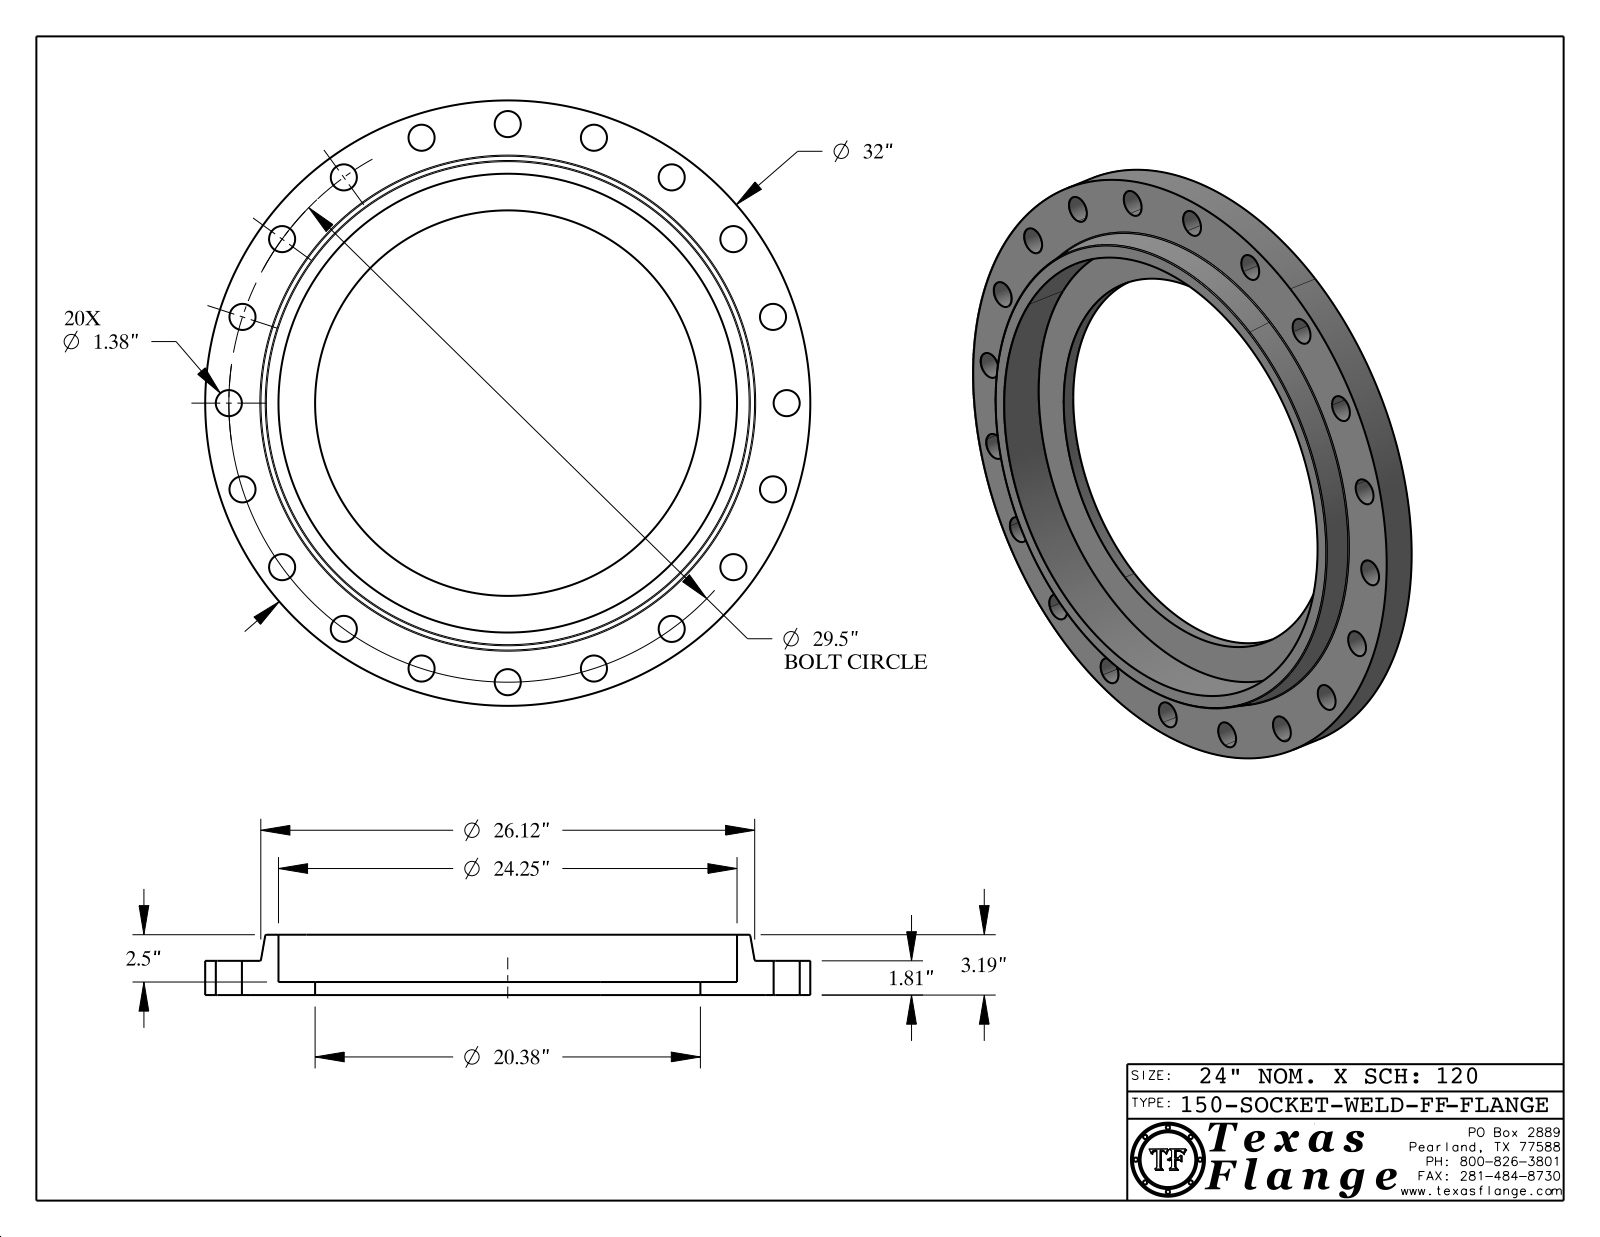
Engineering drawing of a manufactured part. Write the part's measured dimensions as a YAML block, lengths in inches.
part_name: "150-SOCKET-WELD-FF"
step_written_by: "CATIA V5 STEP AP214 (AUTOMOTIVE_DESIGN)"
units: inches
bodies: {solids: 1, faces: 442, planar: 370, cylindrical: 66, other: 6}
overall_size: [32, 32, 3.19]
volume: 747.7
surface_area: 1562
round_holes:
  - {diameter: 1.38, count: 20}
  - {diameter: 0.495, count: 1}
  - {diameter: 20.376, count: 1}
  - {diameter: 24.25, count: 1}
round_bosses_or_shafts:
  - {diameter: 0.03, count: 8}
  - {diameter: 32, count: 1}
  - {diameter: 0.39, count: 1}
face_to_face_distances: [1.81, 0.69, 1.12, 3.19, 2.5, 1.38, 1.795, 1.105, 0.015, 1.395]
hole_center_spacings: [14.75, 29.137, 4.615, 17.34, 20.859, 23.866, 26.285, 9.116]
